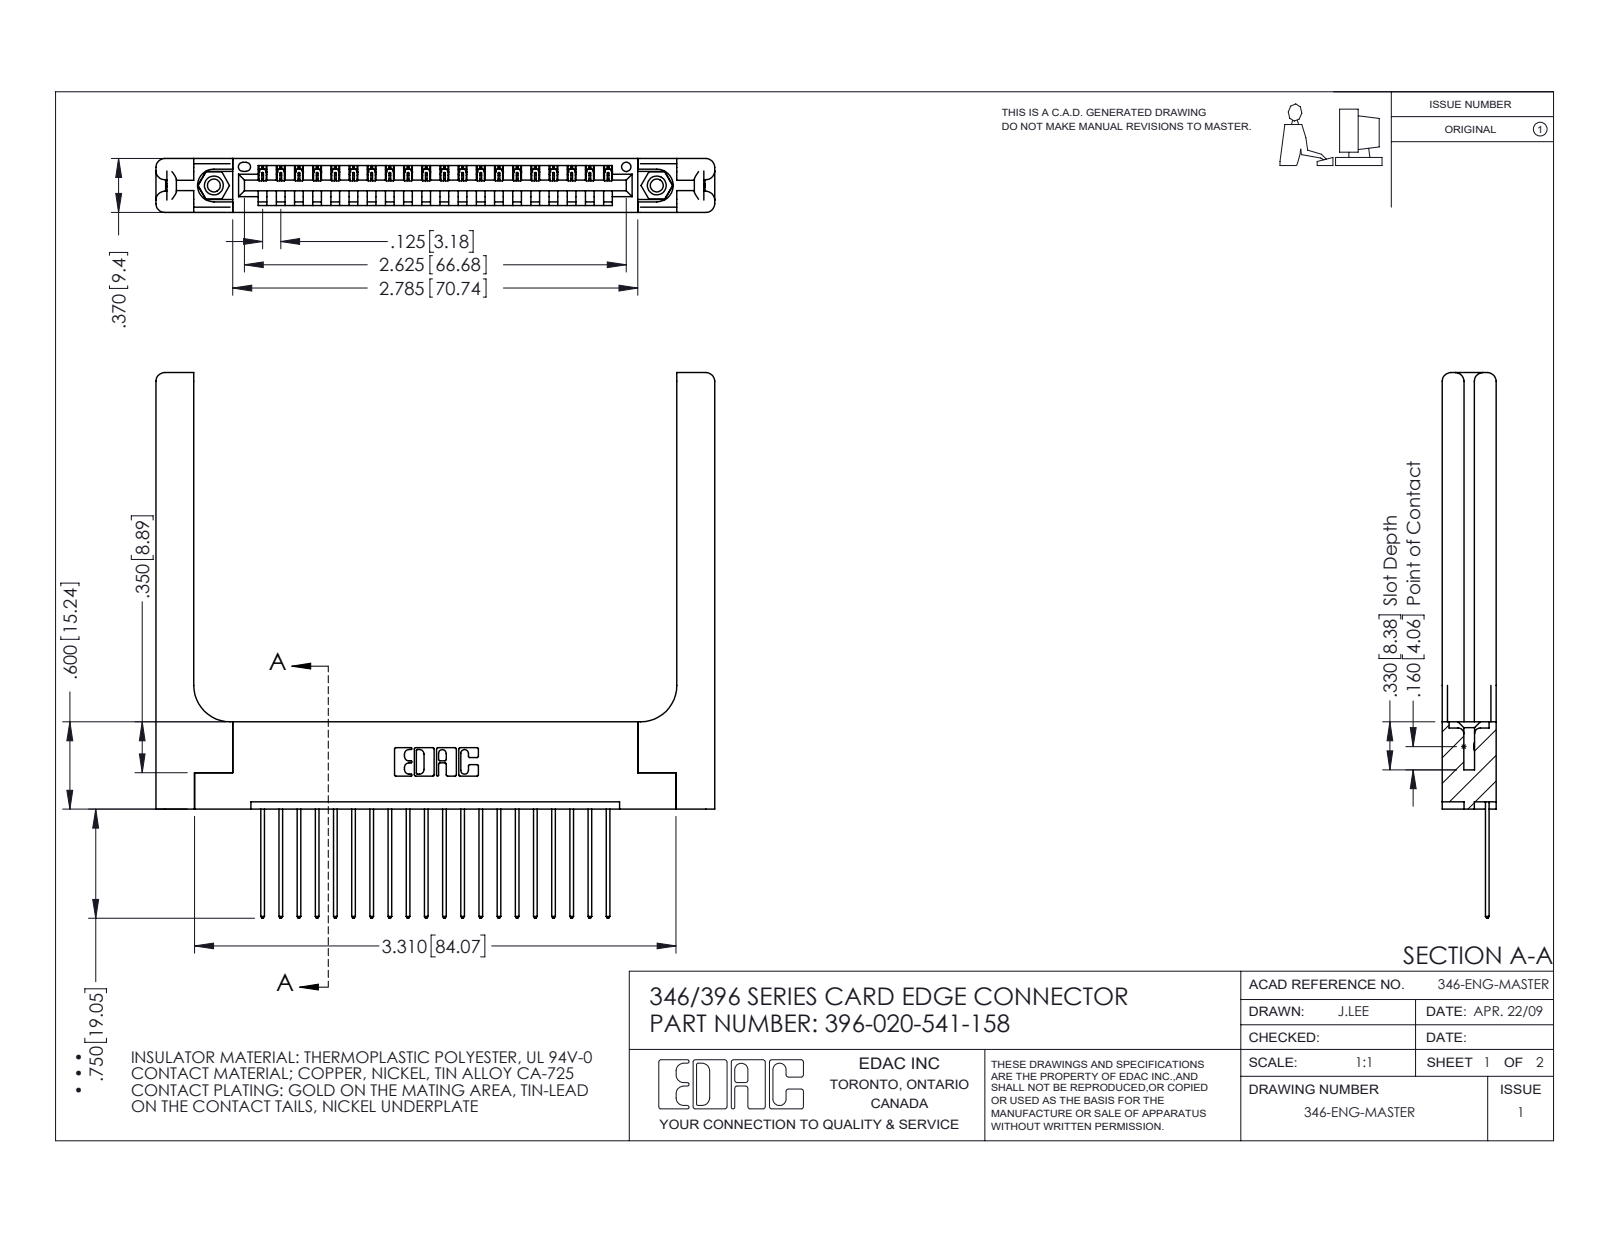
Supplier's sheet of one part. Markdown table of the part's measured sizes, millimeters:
| quantity | value |
| --- | --- |
| part name | 346 Part_Flush Mounting Lugs - 0.156 Dia-TH; 396-020-541-158; 345-250-001_345-250-001-102; 345-292-001_345-293-141 (+1 more) |
| STEP written by | SolidWorks 2016 (CONFIG_CONTROL_DESIGN) |
| units | millimeters |
| bodies | 25 solids, 1538 faces (1024 planar, 454 cylindrical, 60 other) |
| overall size | 97.6 × 95.3 × 9.4 |
| volume | 16 760 mm³ |
| surface area | 16 890 mm² |
| round holes (diameter × count) | 2.3 × 2, 3.2 × 2, 4 × 2, 1.6 × 1 |
| round bosses / shafts (diameter × count) | 3.9 × 2 |
| partial cylindrical surfaces (radius × count) | 0.2 × 40, 0.3 × 40, 0.3 × 22, 1.5 × 16, 0.2 × 6, 0.8 × 6, 0.7 × 3, 0.8 × 2 |
| main face-to-face distances | 9.4, 1.8, 1.2, 8.2, 3.8, 3.8, 6.4, 7.6, 0.6, 2.6 |
| hole center spacings | 6.2, 72.1, 77.3 |
